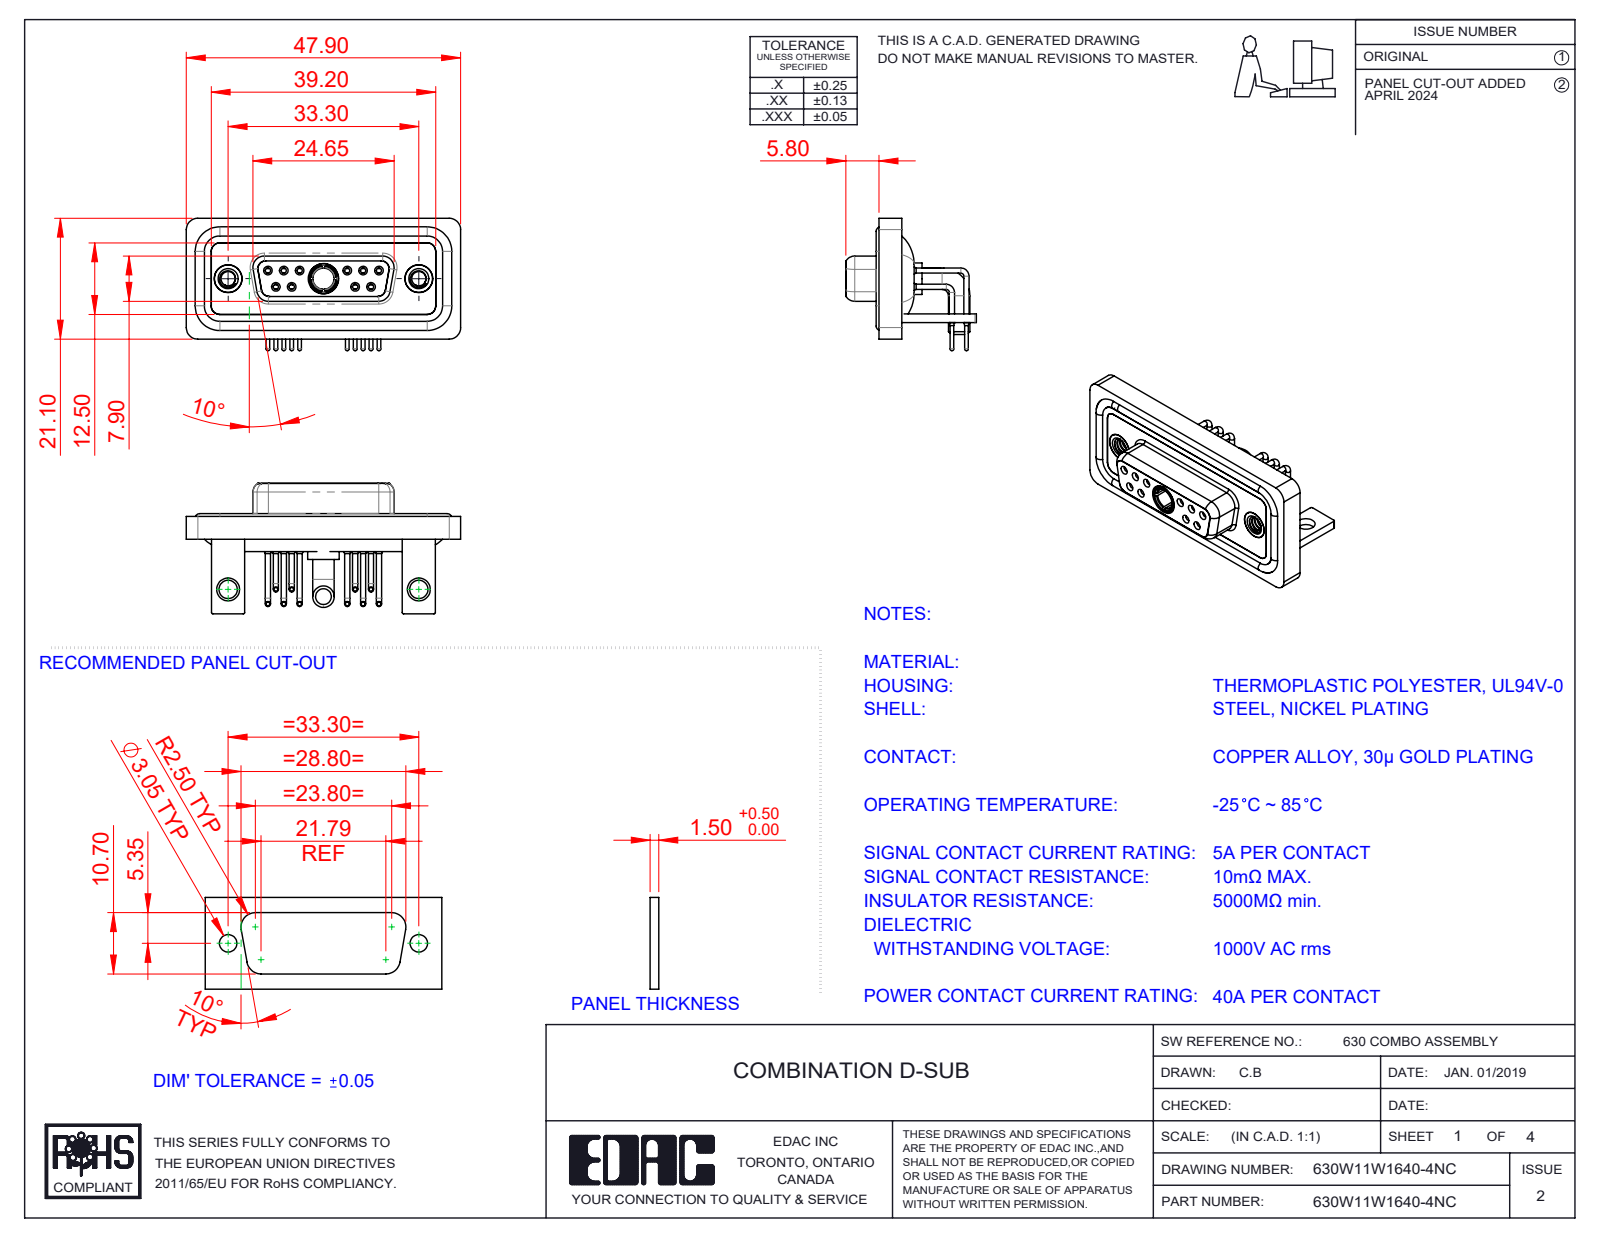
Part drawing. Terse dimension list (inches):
name: 630Combo Shell Front_15 Contacts; Power Socket_40A RA; 630Combo Threaded Rivet_A; 630Combo Shell Rear_15 Contacts (+6 more)
written by: SolidWorks 2023 (CONFIG_CONTROL_DESIGN)
unit: in
bodies: 21 solids, 1036 faces (304 planar, 465 cylindrical, 267 other)
size: 1.886 × 0.91 × 0.898
volume: 0.406 in³; area: 17.44 in²
holes: 10× ⌀0.035, 10× ⌀0.043, 10× ⌀0.059, 10× ⌀0.079, 6× ⌀0.067, 4× ⌀0.063, 3× ⌀0.191, 2× ⌀0.098, 2× ⌀0.126, 2× ⌀0.157, 2× ⌀0.159, 2× ⌀0.197
bosses: 10× ⌀0.063, 10× ⌀0.035, 10× ⌀0.026, 2× ⌀0.195, 2× ⌀0.189, 2× ⌀0.148, 1× ⌀0.217, 1× ⌀0.205
rounds: 21× R0.079, 18× R0.059, 16× R0.01, 12× R0.053, 8× R0.063, 5× R0.02, 4× R0.024, 4× R0.026
face distances: 0.016, 0.114, 0.071, 0.059, 0.146, 0.043, 0.063, 0.161, 0.031, 0.098
hole spacings: 0.124, 0.109, 0.545, 0.436, 0.654, 0.198, 0.198, 0.218
